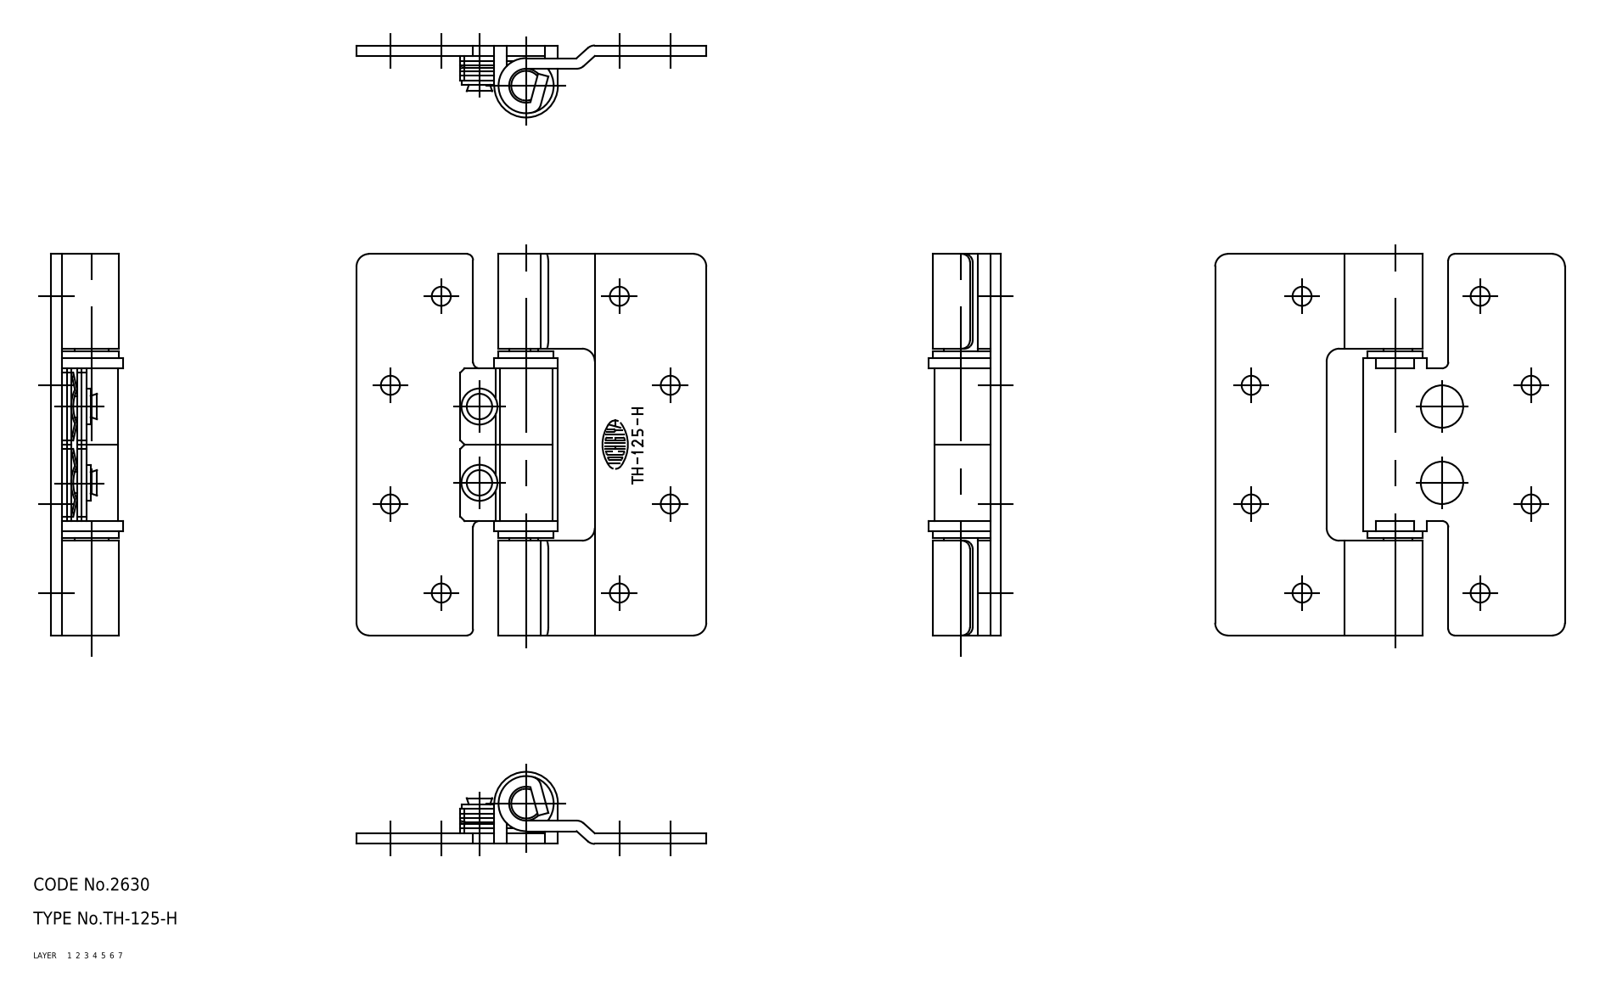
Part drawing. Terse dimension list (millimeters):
name: 67123019; 67123032; 67123045; 67123058 (+8 more)
written by: CADfix (AUTOMOTIVE_DESIGN)
unit: mm
bodies: 15 solids, 270 faces (0 planar, 0 cylindrical, 270 other)
size: 90 × 82.5 × 17
volume: 27 456 mm³; area: 29 893 mm²
